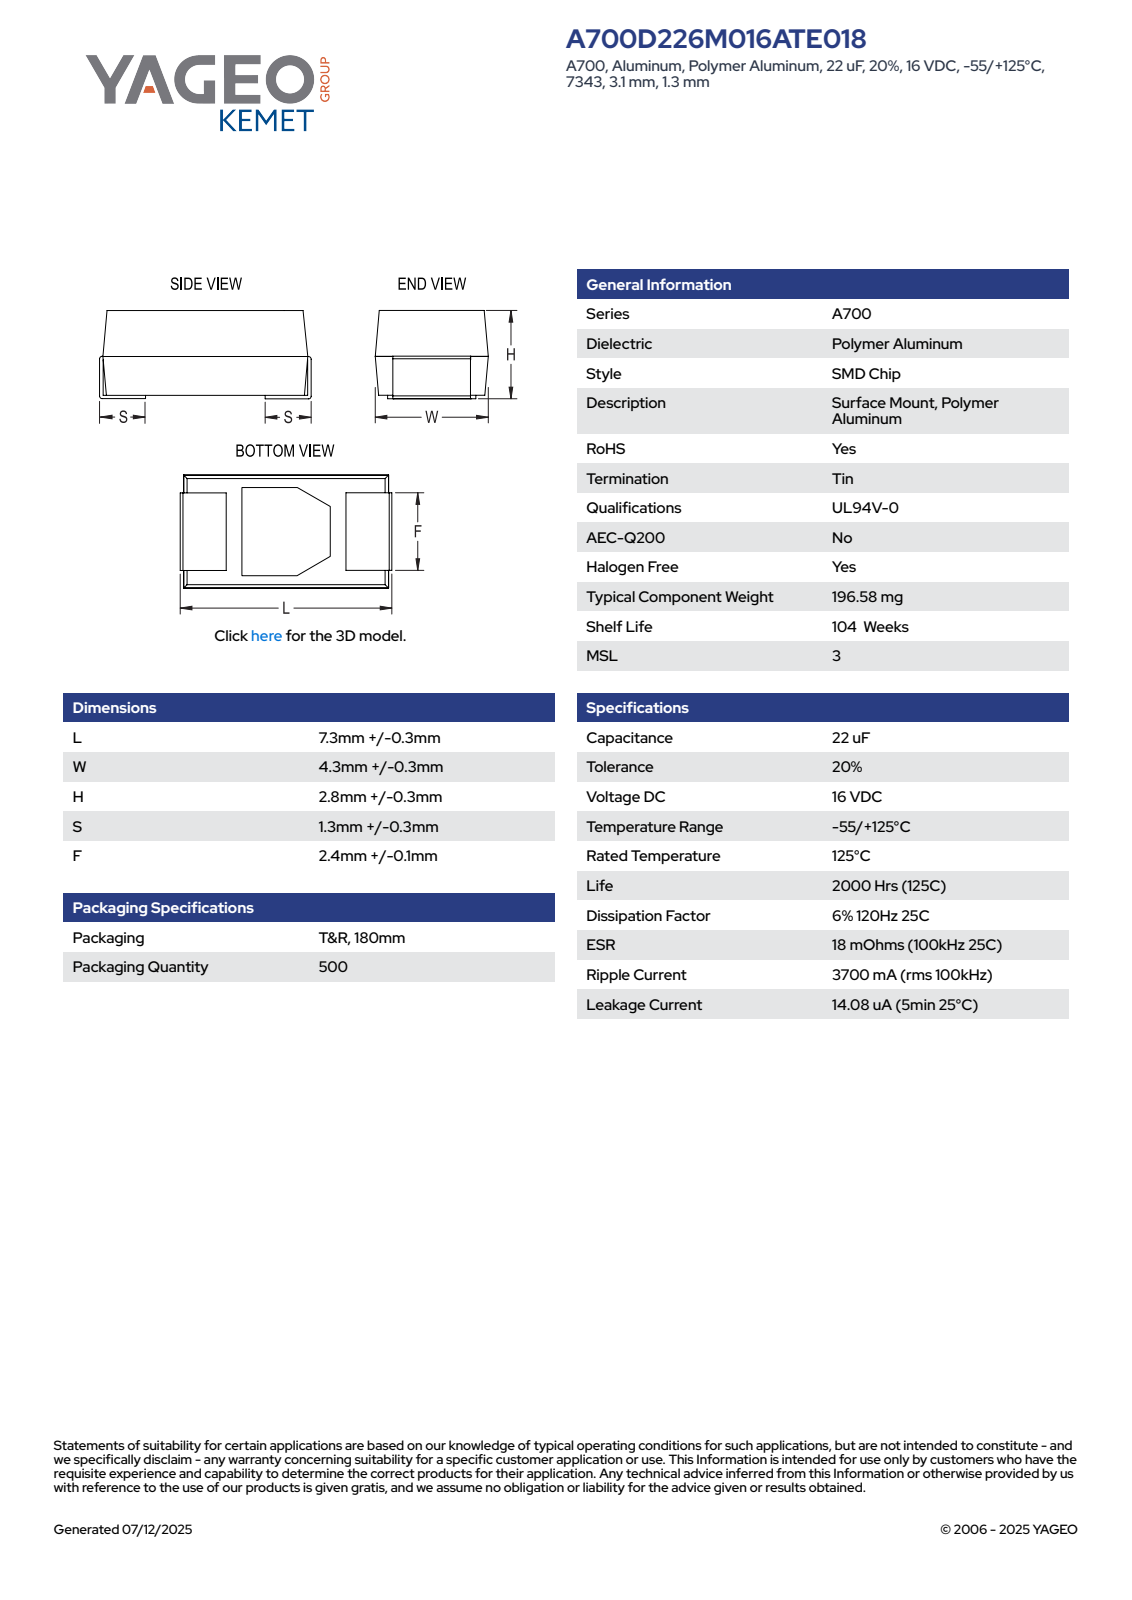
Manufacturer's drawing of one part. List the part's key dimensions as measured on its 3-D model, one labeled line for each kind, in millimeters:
Part name (STEP PRODUCT): CAS_SMD_L7.6W4.6H3.1S1.3F2.5
STEP written by: SolidWorks 2021 (AUTOMOTIVE_DESIGN)
Units: millimetres
Bodies: 1 solid, 82 faces (78 planar, 4 cylindrical, 0 other)
Overall size (bounding box): 7.6 × 4.6 × 3.1
Volume: 96 mm³ · Surface area: 152 mm²
Partial cylindrical surfaces — rounded edges, fillets, slot ends (radius × count): R0.1 ×4
Main face-to-face distances: 3, 4.56, 3.1, 7.5, 7.29, 7.3, 7.4, 7.6, 1.64, 5.96
